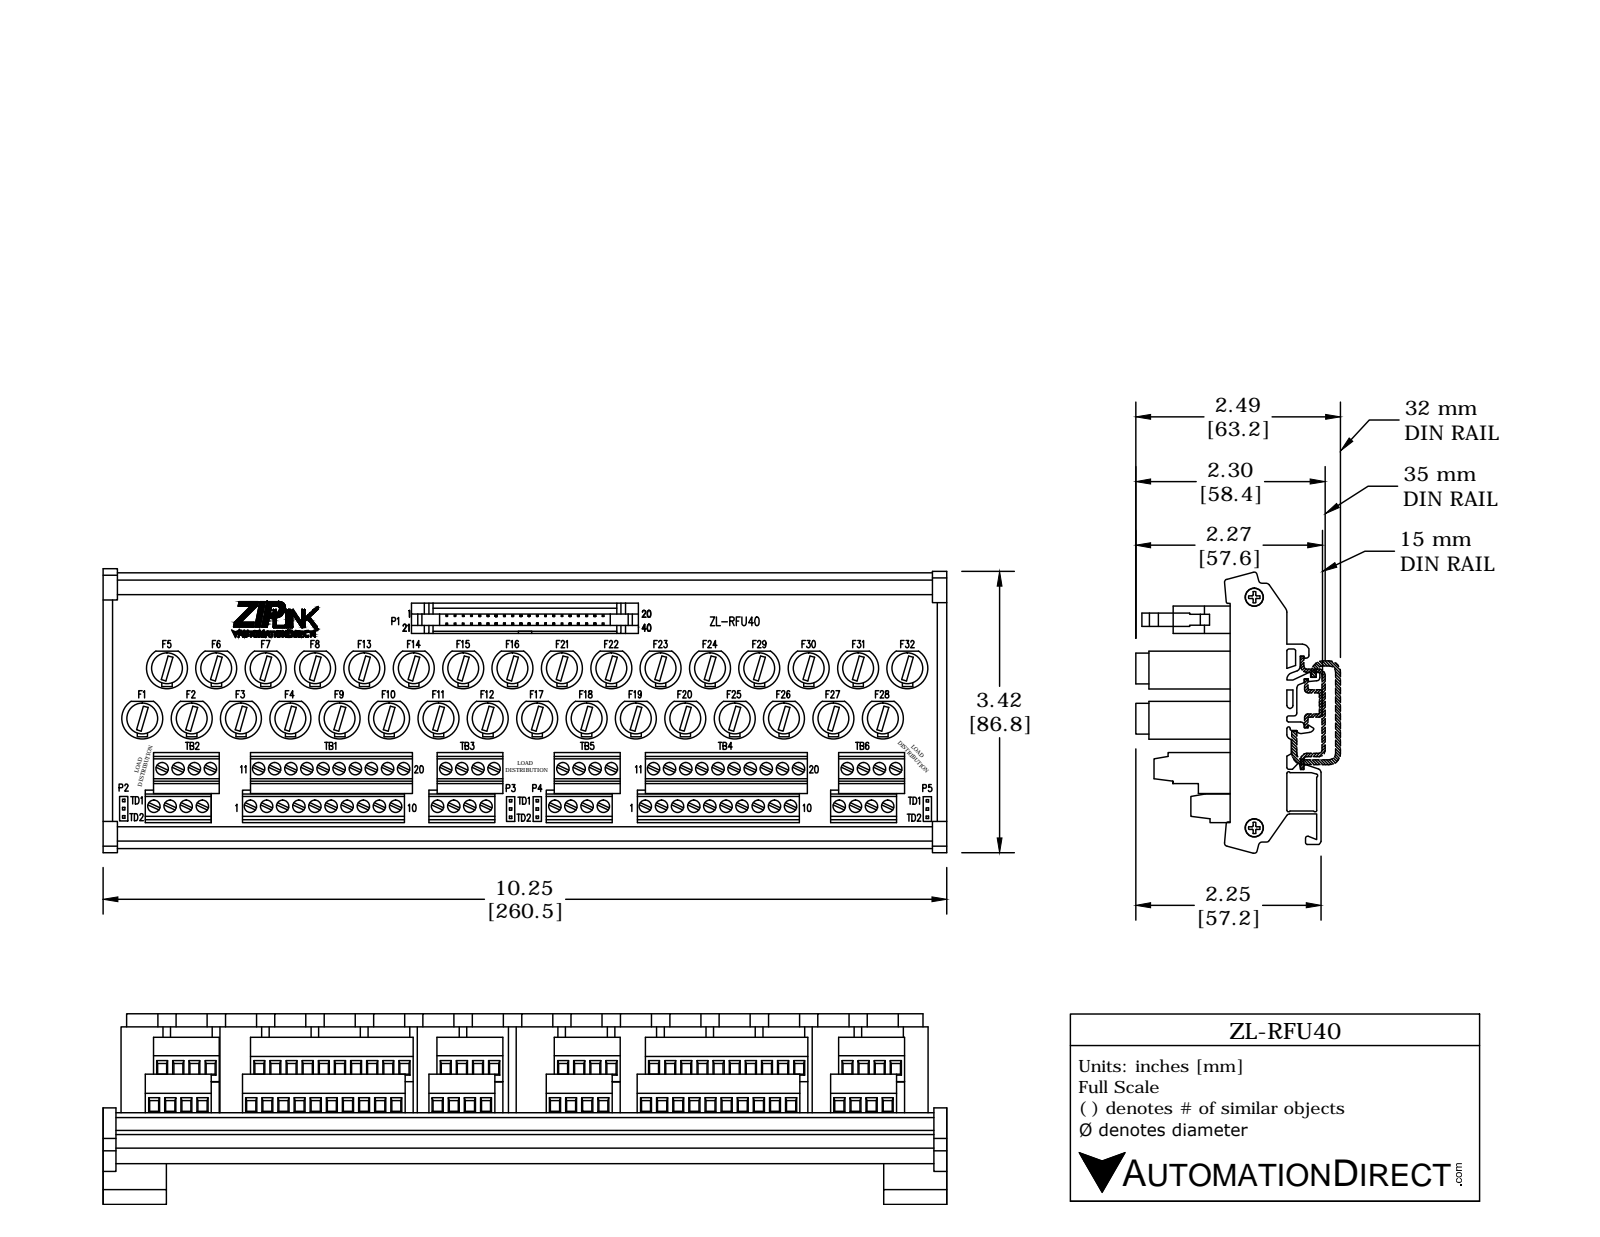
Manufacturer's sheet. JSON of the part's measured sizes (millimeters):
{"part_name": "ZL-RFU40", "step_written_by": "SolidWorks 2014 (AUTOMOTIVE_DESIGN)", "units": "millimeters", "bodies": {"solids": 1, "faces": 2309, "planar": 1822, "cylindrical": 413, "other": 74}, "overall_size": [262, 86.9, 60.5], "volume_mm3": 348900, "surface_area_mm2": 159500, "round_holes": [[3.8, 64], [5.7, 2]], "round_bosses_or_shafts": [[0.8, 40], [9.7, 16], [9.1, 16], [8.9, 16], [8.3, 16], [5.2, 2]], "partial_cylinders_radius": [[0.4, 41], [0.8, 10], [1.5, 4]], "face_to_face_distances": [11, 3.5, 14.5, 16, 12.5, 1.4, 14, 0.8, 16.7, 13.2], "hole_center_spacings": [5, 24.9, 29.9, 10, 19.9, 12.4, 34.8, 12.4]}
